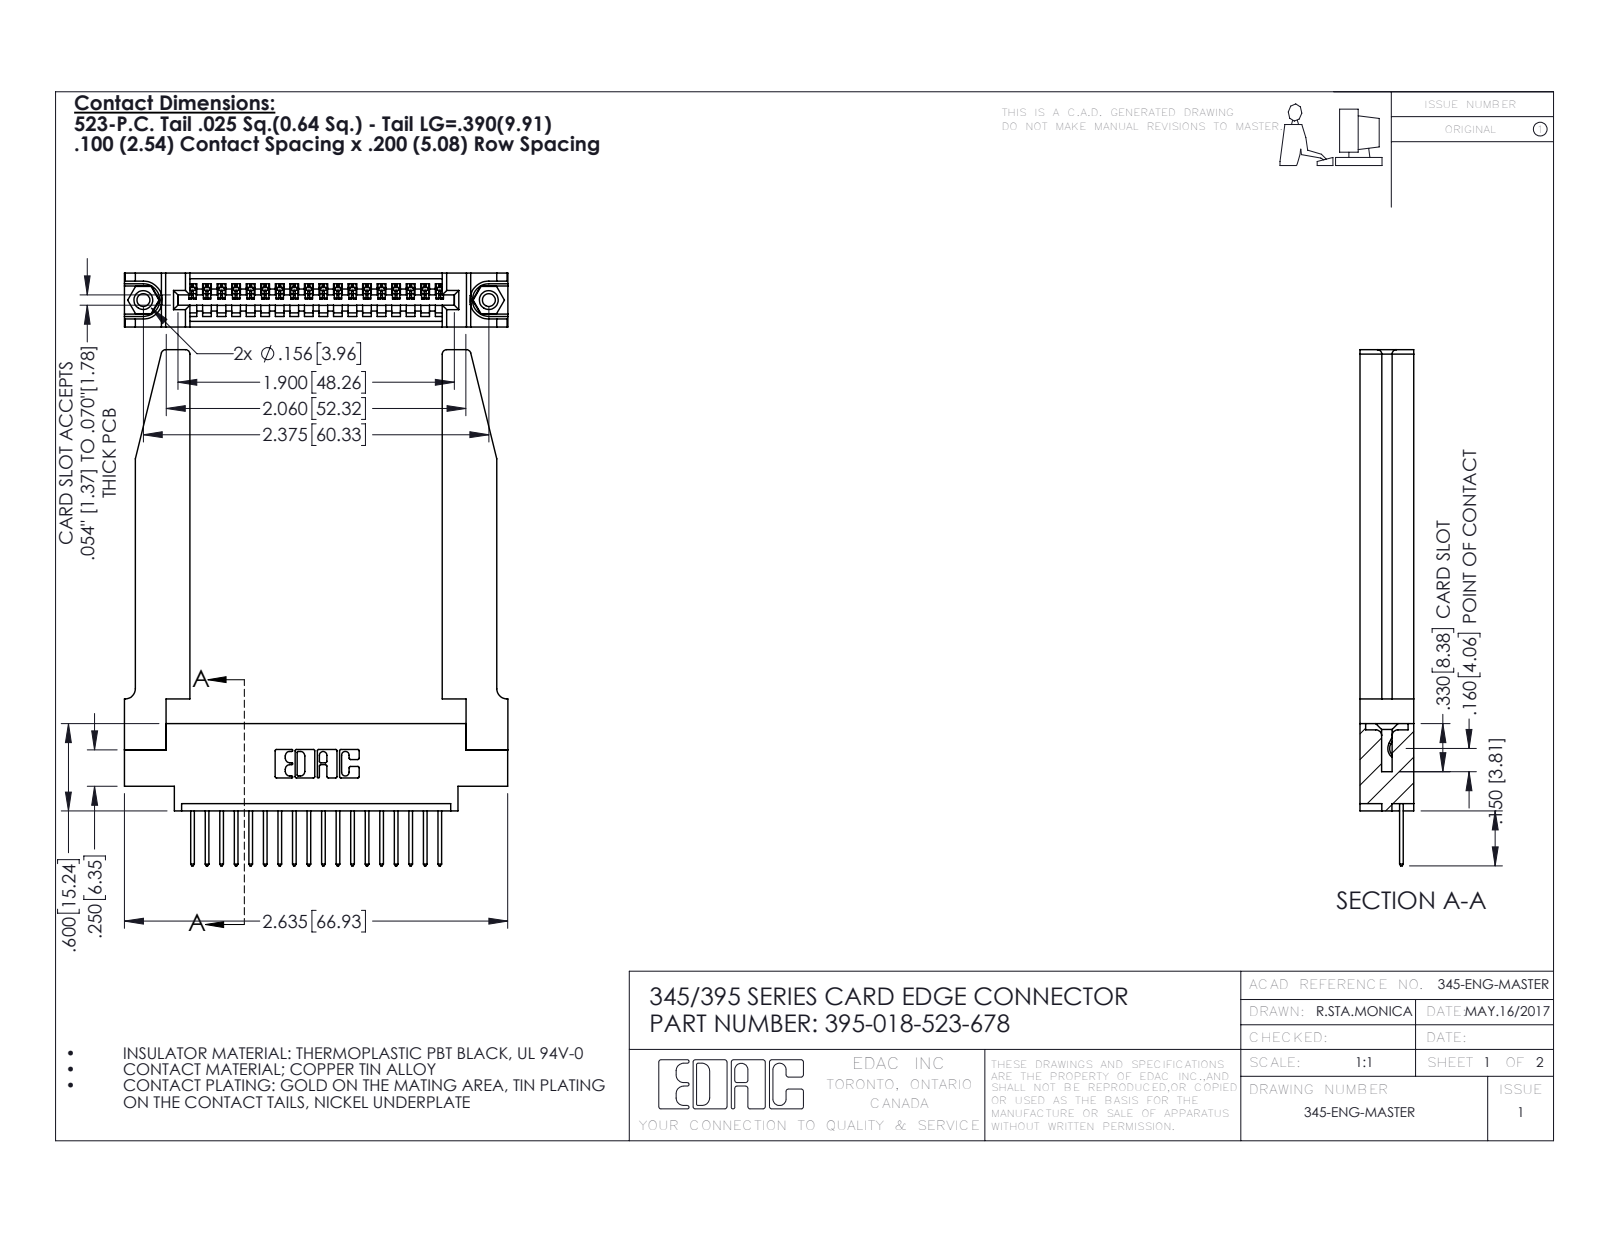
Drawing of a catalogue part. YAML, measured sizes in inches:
part_name: "345 Part_0.170 Offset - 0.156 Dia-TH; 345-250-001_345-250-001-102; 395-018-523-678; 345-292-001_345-293-123 (+1 more)"
step_written_by: "SolidWorks 2016 (CONFIG_CONTROL_DESIGN)"
units: inches
bodies: {solids: 23, faces: 1408, planar: 946, cylindrical: 410, other: 52}
overall_size: [3.547, 2.636, 0.37]
volume: 0.843
surface_area: 22.78
round_holes:
  - {diameter: 0.089, count: 2}
  - {diameter: 0.125, count: 2}
  - {diameter: 0.156, count: 2}
  - {diameter: 0.064, count: 1}
round_bosses_or_shafts:
  - {diameter: 0.155, count: 2}
partial_cylinders:
  - {radius: 0.006, count: 36}
  - {radius: 0.01, count: 36}
  - {radius: 0.01, count: 22}
  - {radius: 0.03, count: 8}
  - {radius: 0.007, count: 6}
  - {radius: 0.031, count: 6}
  - {radius: 0.026, count: 3}
  - {radius: 0.031, count: 2}
face_to_face_distances: [0.37, 0.072, 0.298, 0.098, 0.272, 0.025, 0.15, 0.148, 0.2, 0.22]
hole_center_spacings: [0.27, 2.141, 2.375]
